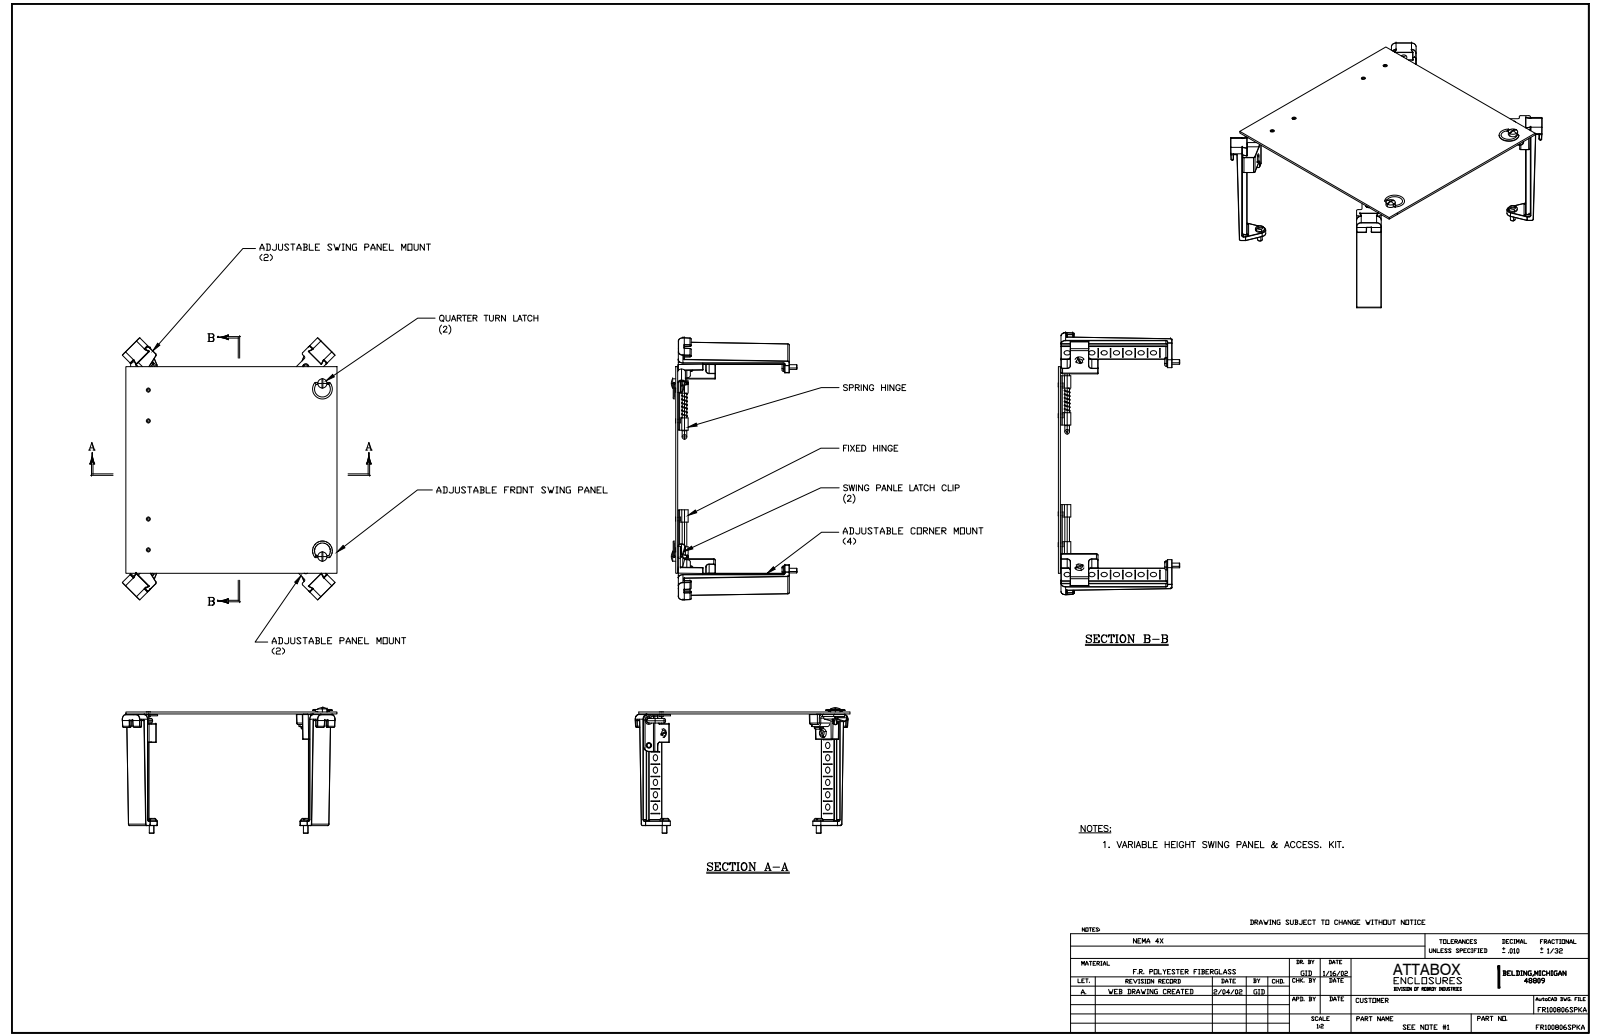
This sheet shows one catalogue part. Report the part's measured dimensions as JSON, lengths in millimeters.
{"part_name": "FR100806SPKA", "step_written_by": "SolidWorks 2019 (AUTOMOTIVE_DESIGN)", "units": "millimeters", "bodies": {"solids": 50, "faces": 1825, "planar": 840, "cylindrical": 485, "other": 500}, "overall_size": [269.8, 219, 119.5], "volume_mm3": 241100, "surface_area_mm2": 180200, "round_holes": [[6.4, 36], [4, 6], [6.4, 6], [1.3, 4], [3.6, 4], [3.7, 4], [5.5, 4], [5.6, 4], [7.9, 3], [2, 2], [3.9, 2], [5, 2]], "round_bosses_or_shafts": [[4.8, 12], [9.5, 8], [6.2, 6], [11, 4], [8, 4], [4.1, 4], [2, 4], [4.7, 3]], "partial_cylinders_radius": [[0.3, 214], [1.5, 44], [1.6, 11], [0.6, 8], [3.3, 8], [1.6, 7], [1.2, 4], [3.2, 4]], "face_to_face_distances": [2, 286.9, 5.2, 292, 2, 174.1, 112.8, 138.2, 148.7, 35.9], "hole_center_spacings": [38.1, 12.7, 25.4, 44, 52.3, 35.9, 50.8, 62.2]}
